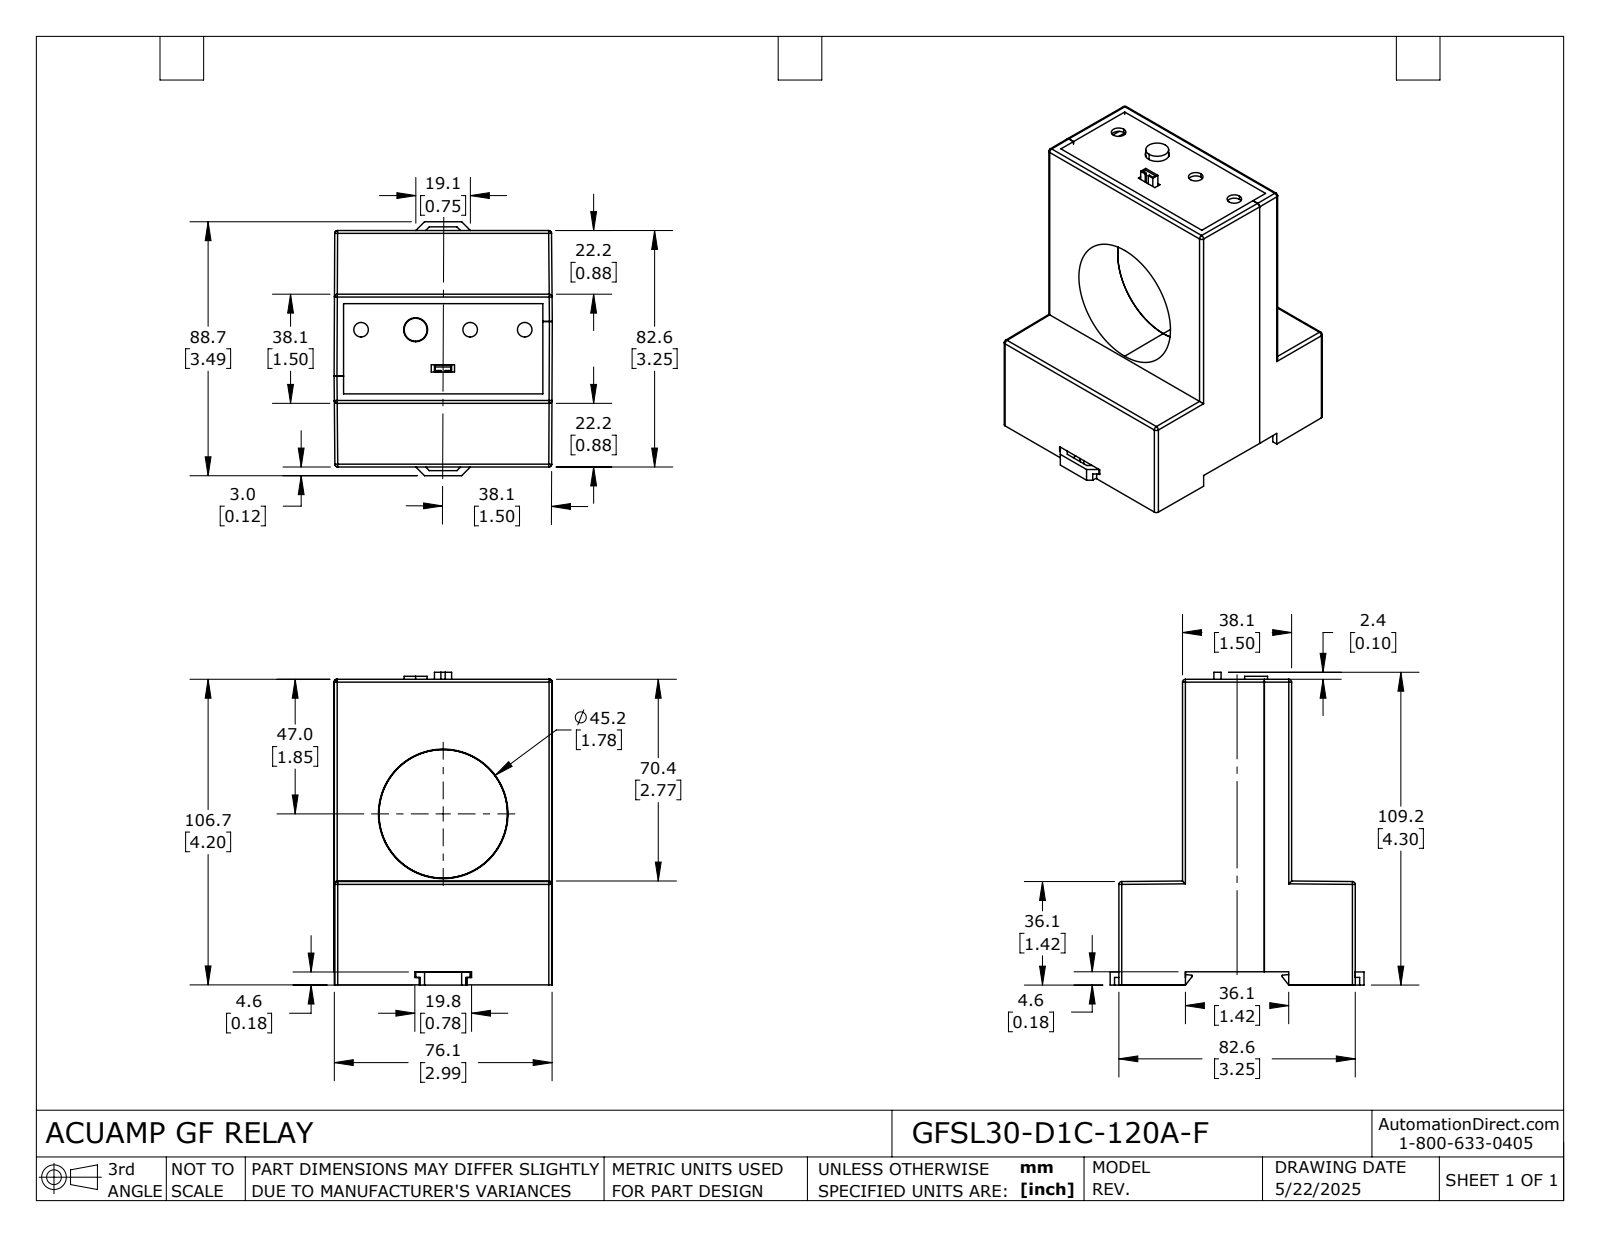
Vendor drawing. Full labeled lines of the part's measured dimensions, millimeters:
Part name (STEP PRODUCT): GFSL30-D1C-120A-F
STEP written by: SolidWorks 2024 (AUTOMOTIVE_DESIGN)
Units: millimetres
Bodies: 8 solids, 1046 faces (890 planar, 120 cylindrical, 36 other)
Overall size (bounding box): 109.2 × 88.6 × 76.2
Volume: 90 690 mm³ · Surface area: 99 290 mm²
Round holes (diameter × count): ⌀5.1 ×7, ⌀8.4 ×4, ⌀3 ×2
Round bosses / shafts (diameter × count): ⌀2.5 ×2, ⌀8 ×1
Partial cylindrical surfaces — rounded edges, fillets, slot ends (radius × count): R0.5 ×23, R1 ×20, R0.2 ×4, R0.3 ×4, R2.6 ×4, R4.6 ×4
Main face-to-face distances: 2, 22.2, 58.3, 36.1, 74.1, 2, 76.1, 38.1, 20.2, 56.3
Hole centre spacings: 19.1, 23.3, 38.1, 13.5, 40.4, 57.2, 58.7, 25.2
